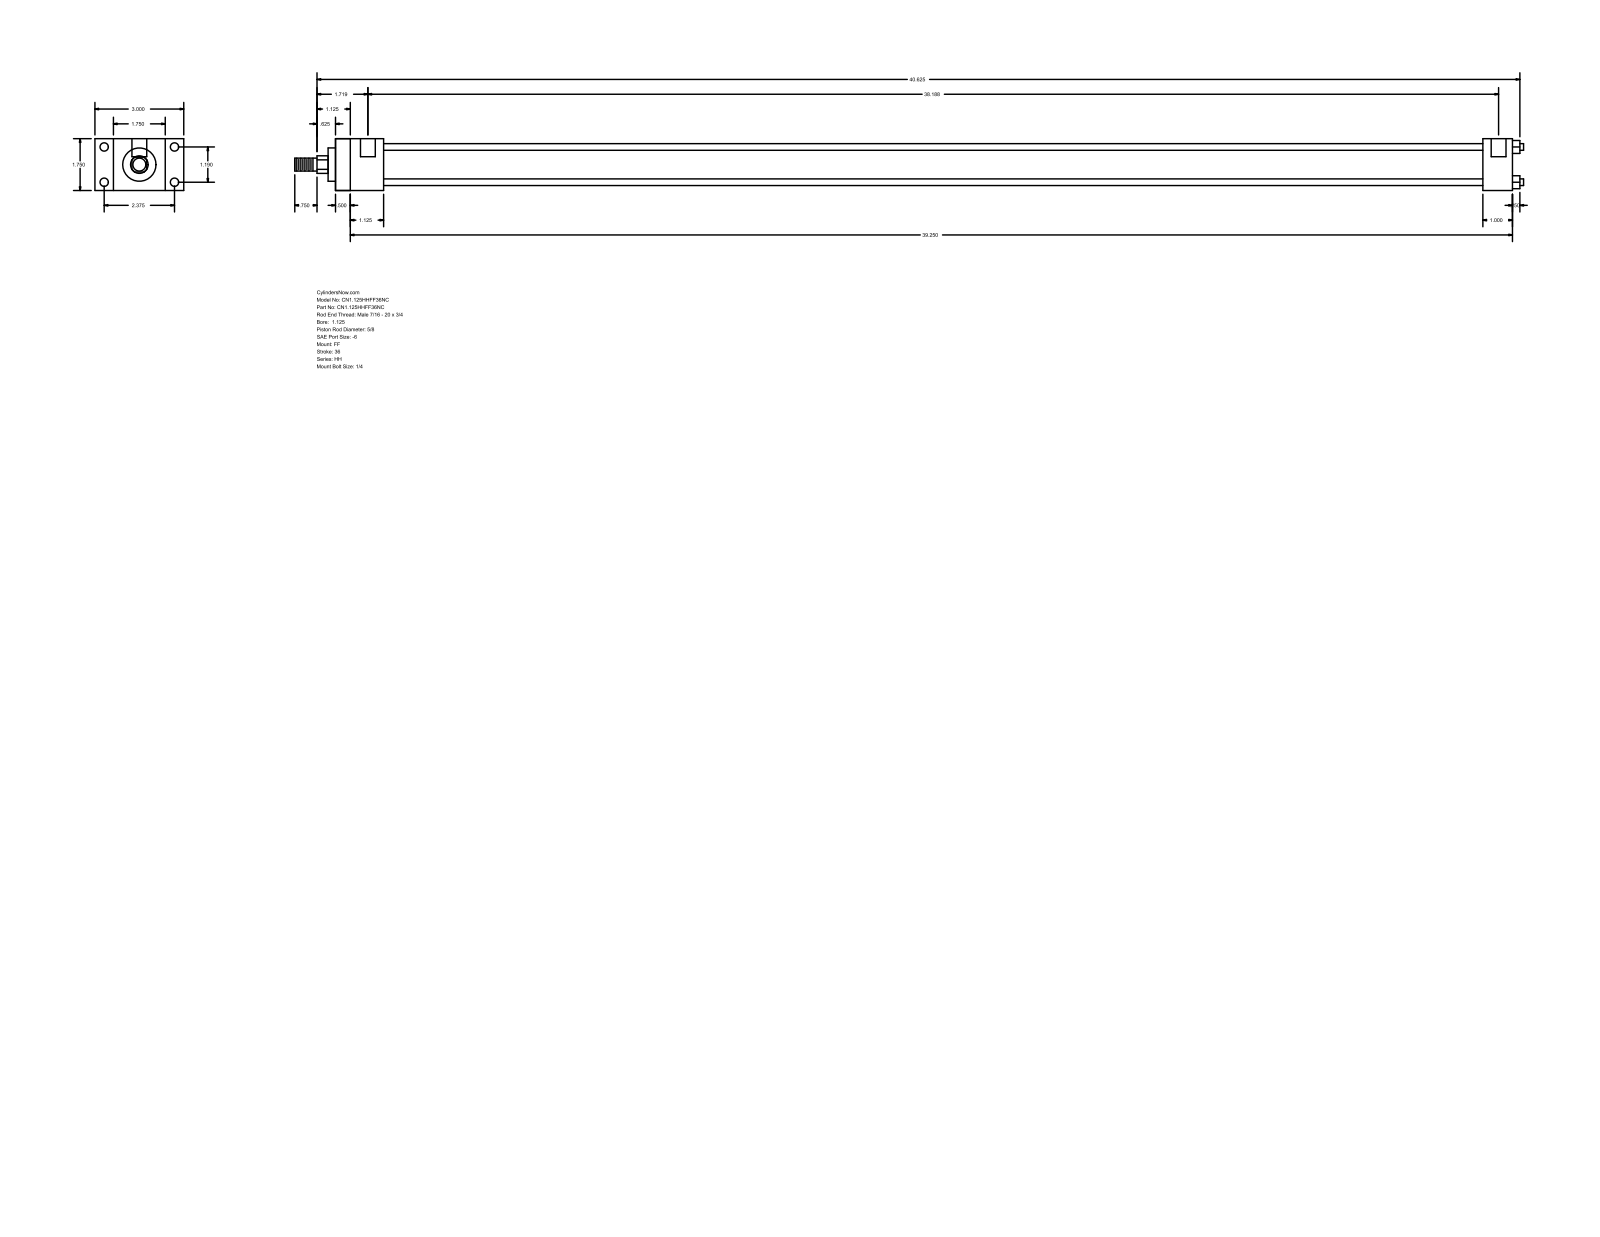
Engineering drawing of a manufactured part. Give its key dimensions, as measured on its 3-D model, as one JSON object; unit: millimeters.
{"part_name": "HH_FF__0112_0.625", "step_written_by": "GSSL Pune (CONFIG_CONTROL_DESIGN)", "units": "millimeters", "bodies": {"solids": 0, "faces": 92, "planar": 64, "cylindrical": 28, "other": 0}, "overall_size": [1054.1, 76.2, 44.45], "round_holes": [[5.56, 4], [7.14, 4], [12.7, 2]], "round_bosses_or_shafts": [[5.71, 4], [34.92, 1], [28.57, 1], [15.88, 1], [11.11, 1]], "partial_cylinders_radius": [[7.54, 1]], "face_to_face_distances": [44.46, 1009.65, 15.87, 12.69, 996.96, 28.58, 60.33, 41.27, 984.24, 971.55], "hole_center_spacings": [30.22, 60.32, 67.47, 966.79, 3.17, 969.96]}
